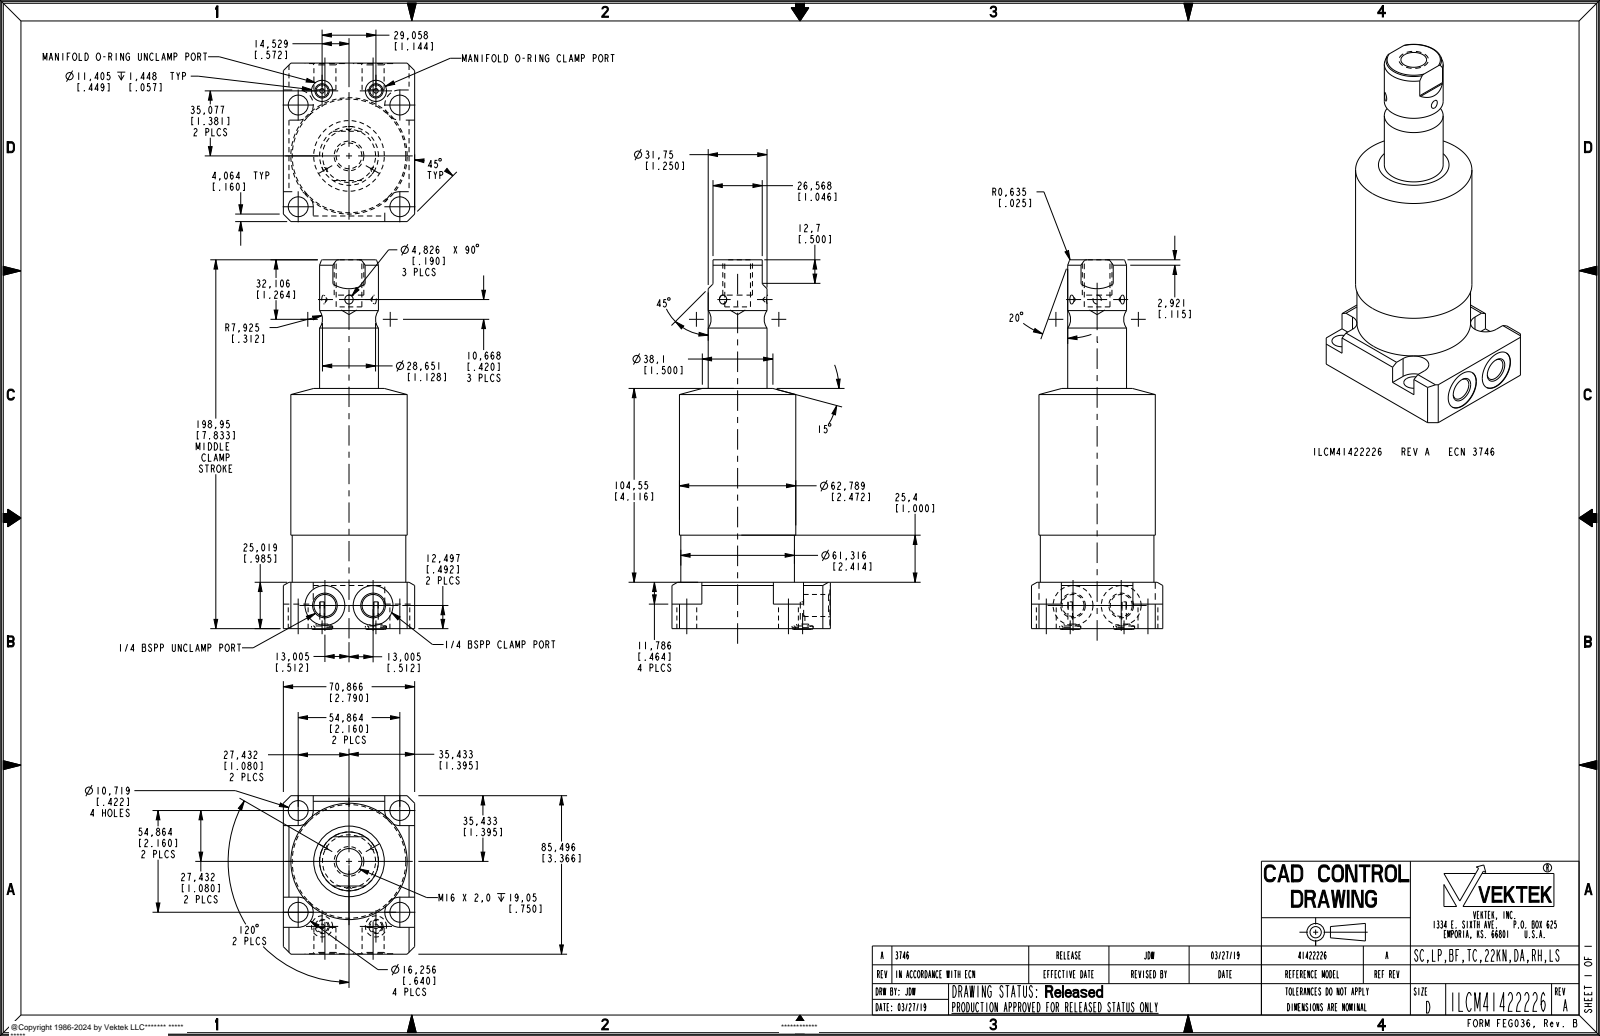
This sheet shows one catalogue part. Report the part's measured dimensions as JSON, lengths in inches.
{"part_name": "ILCM41422226", "step_written_by": "PRO/ENGINEER BY PARAMETRIC TECHNOLOGY CORPORATION, 2013320 (AUTOMOTIVE_DESIGN)", "units": "inches", "bodies": {"solids": 1, "faces": 124, "planar": 48, "cylindrical": 48, "other": 28}, "overall_size": [7.849, 3.366, 2.79], "volume_in3": 30.29, "surface_area_in2": 80.42, "round_holes": [[0.422, 4], [0.098, 2], [0.256, 2], [0.449, 2], [0.468, 2], [0.846, 2], [0.546, 1]], "round_bosses_or_shafts": [[2.472, 1], [2.414, 1], [1.25, 1], [0.63, 1]], "partial_cylinders_radius": [[0.32, 4], [0.03, 2]], "face_to_face_distances": [0.985, 2.79, 3.366, 0.464, 0.521, 6.848, 7.312, 7.833, 3.356, 2.155], "hole_center_spacings": [1.527, 2.16, 0.591, 1.495, 1.679, 2.513, 2.964, 3.054]}
